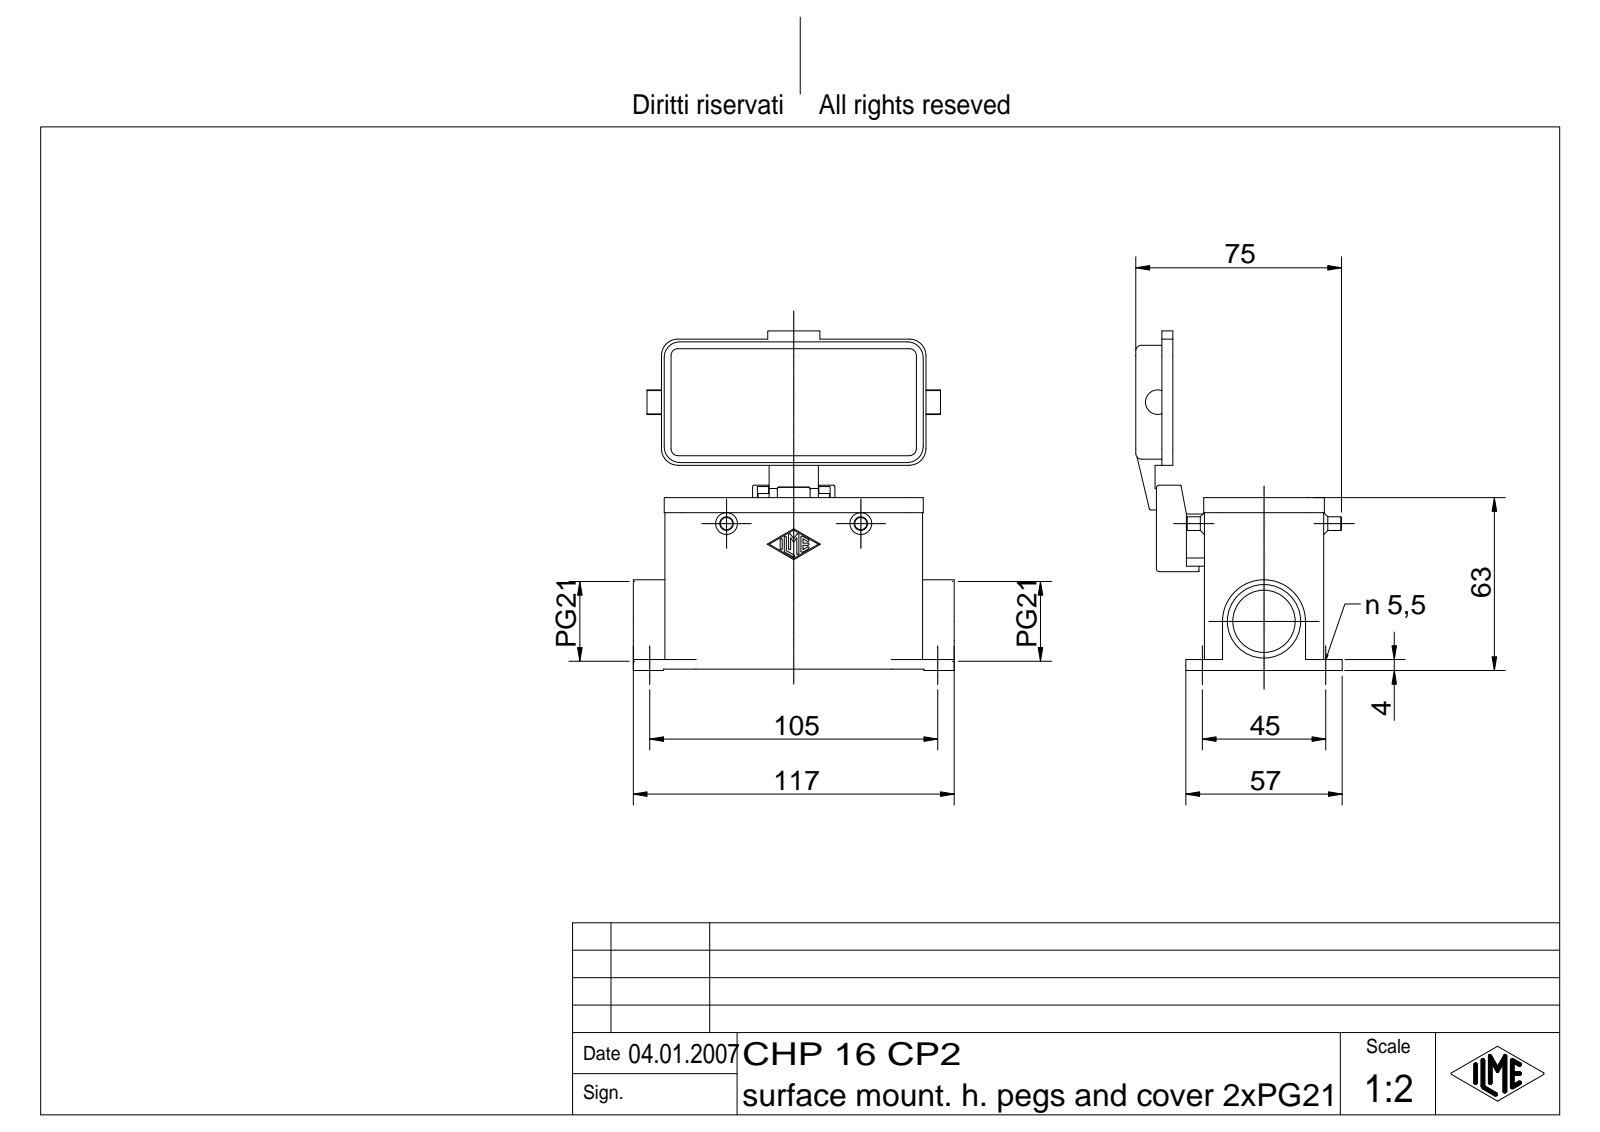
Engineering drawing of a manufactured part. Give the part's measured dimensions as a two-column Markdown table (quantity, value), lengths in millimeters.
| quantity | value |
| --- | --- |
| part name | CHP 16 CP2 |
| STEP written by | Autodesk Inventor 7 (AUTOMOTIVE_DESIGN) |
| units | millimeters |
| bodies | 1 solid, 469 faces (195 planar, 164 cylindrical, 110 other) |
| overall size | 123.75 × 117 × 75.25 |
| volume | 108 626 mm³ |
| surface area | 67 349 mm² |
| round holes (diameter × count) | 5.5 × 4, 4 × 1, 5 × 1, 22.78 × 1, 26.78 × 1 |
| round bosses / shafts (diameter × count) | 5 × 2, 3 × 2, 7 × 1, 4 × 1 |
| partial cylindrical surfaces (radius × count) | 0.38 × 14, 1 × 14, 6 × 12, 0.5 × 10, 0.7 × 8, 2 × 8, 2.5 × 4, 3 × 4 |
| main face-to-face distances | 3, 40.5, 43.5, 2.5, 63, 37.5, 3.5, 22.5, 66, 25.5 |
| hole center spacings | 45, 105, 114.24 |
